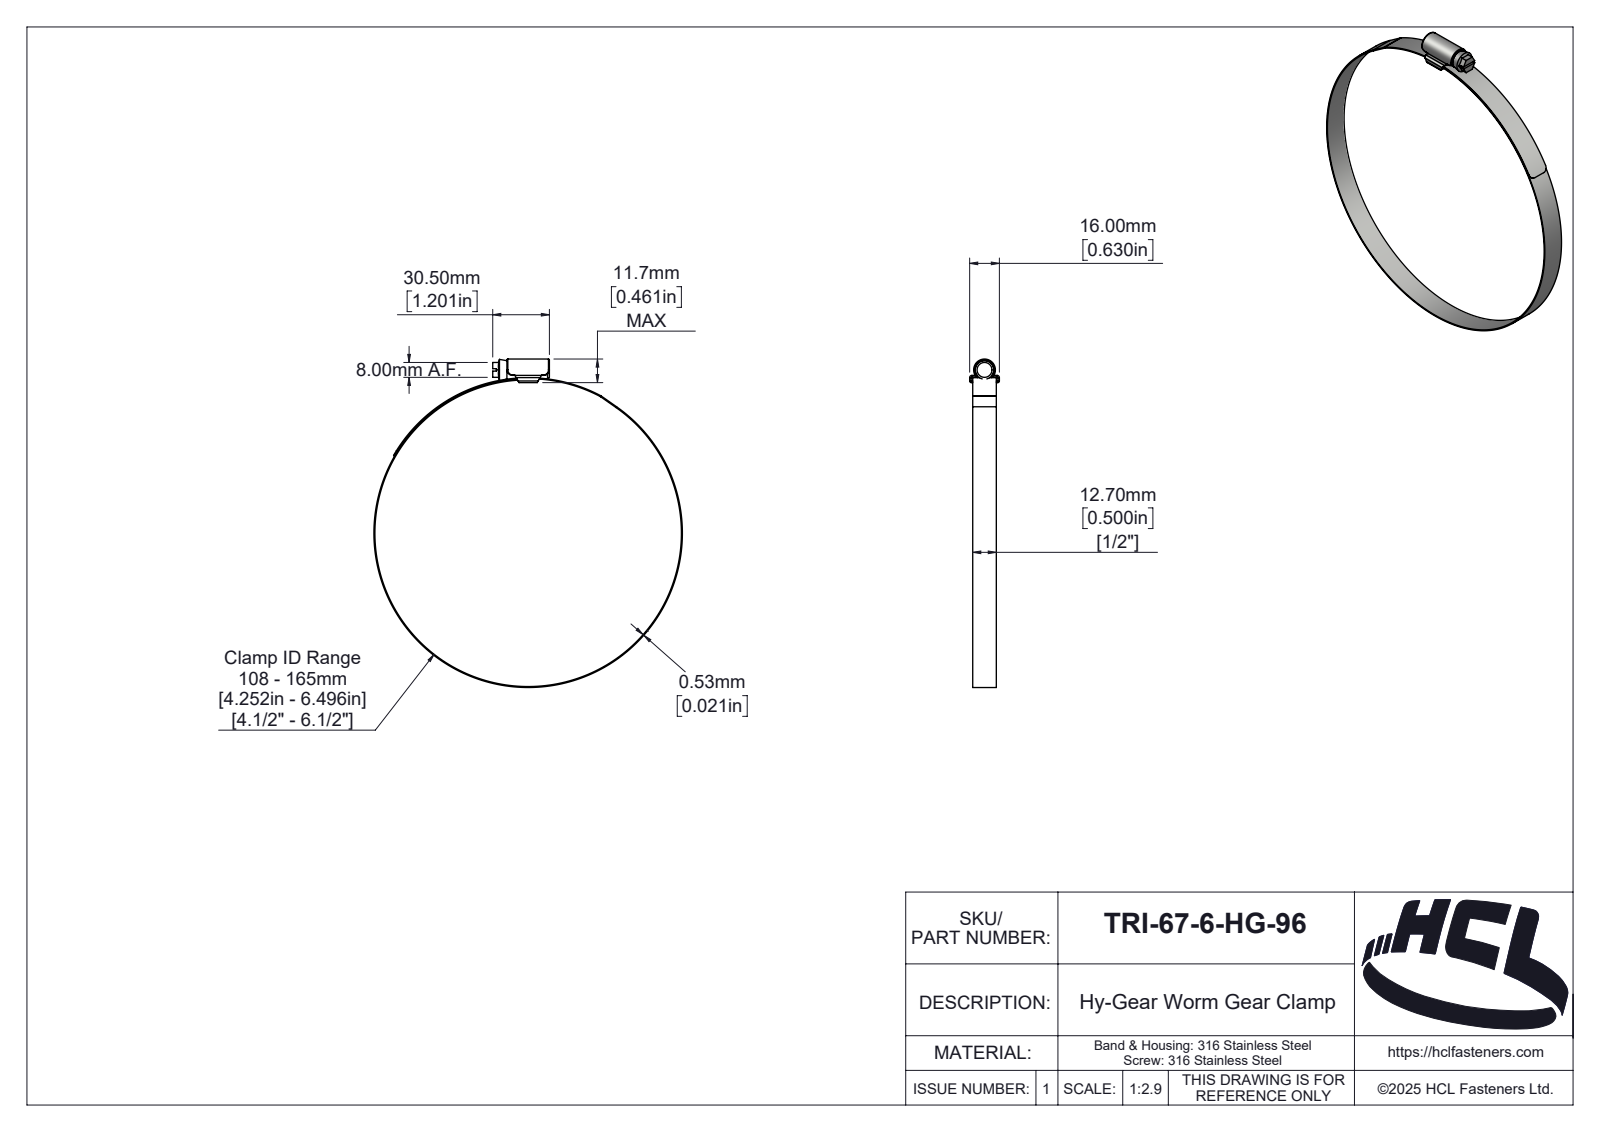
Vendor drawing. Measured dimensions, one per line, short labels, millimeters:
name: TRI-57-0-HG-96
written by: SolidWorks 2025 (AUTOMOTIVE_DESIGN)
unit: mm
bodies: 3 solids, 189 faces (39 planar, 89 cylindrical, 61 other)
size: 176.73 × 166.06 × 16
volume: 7 081 mm³; area: 18 984 mm²
holes: 1× ⌀165
bosses: 1× ⌀166.06, 1× ⌀10
rounds: 6× R0.5, 4× R3, 2× R0.1, 2× R0.9, 2× R1.2, 1× R0.46, 1× R1.89, 1× R2
face distances: 12.7, 0.8, 3.1, 0.53, 2.3, 3.9, 30.5, 1.65, 14.35, 15.2
